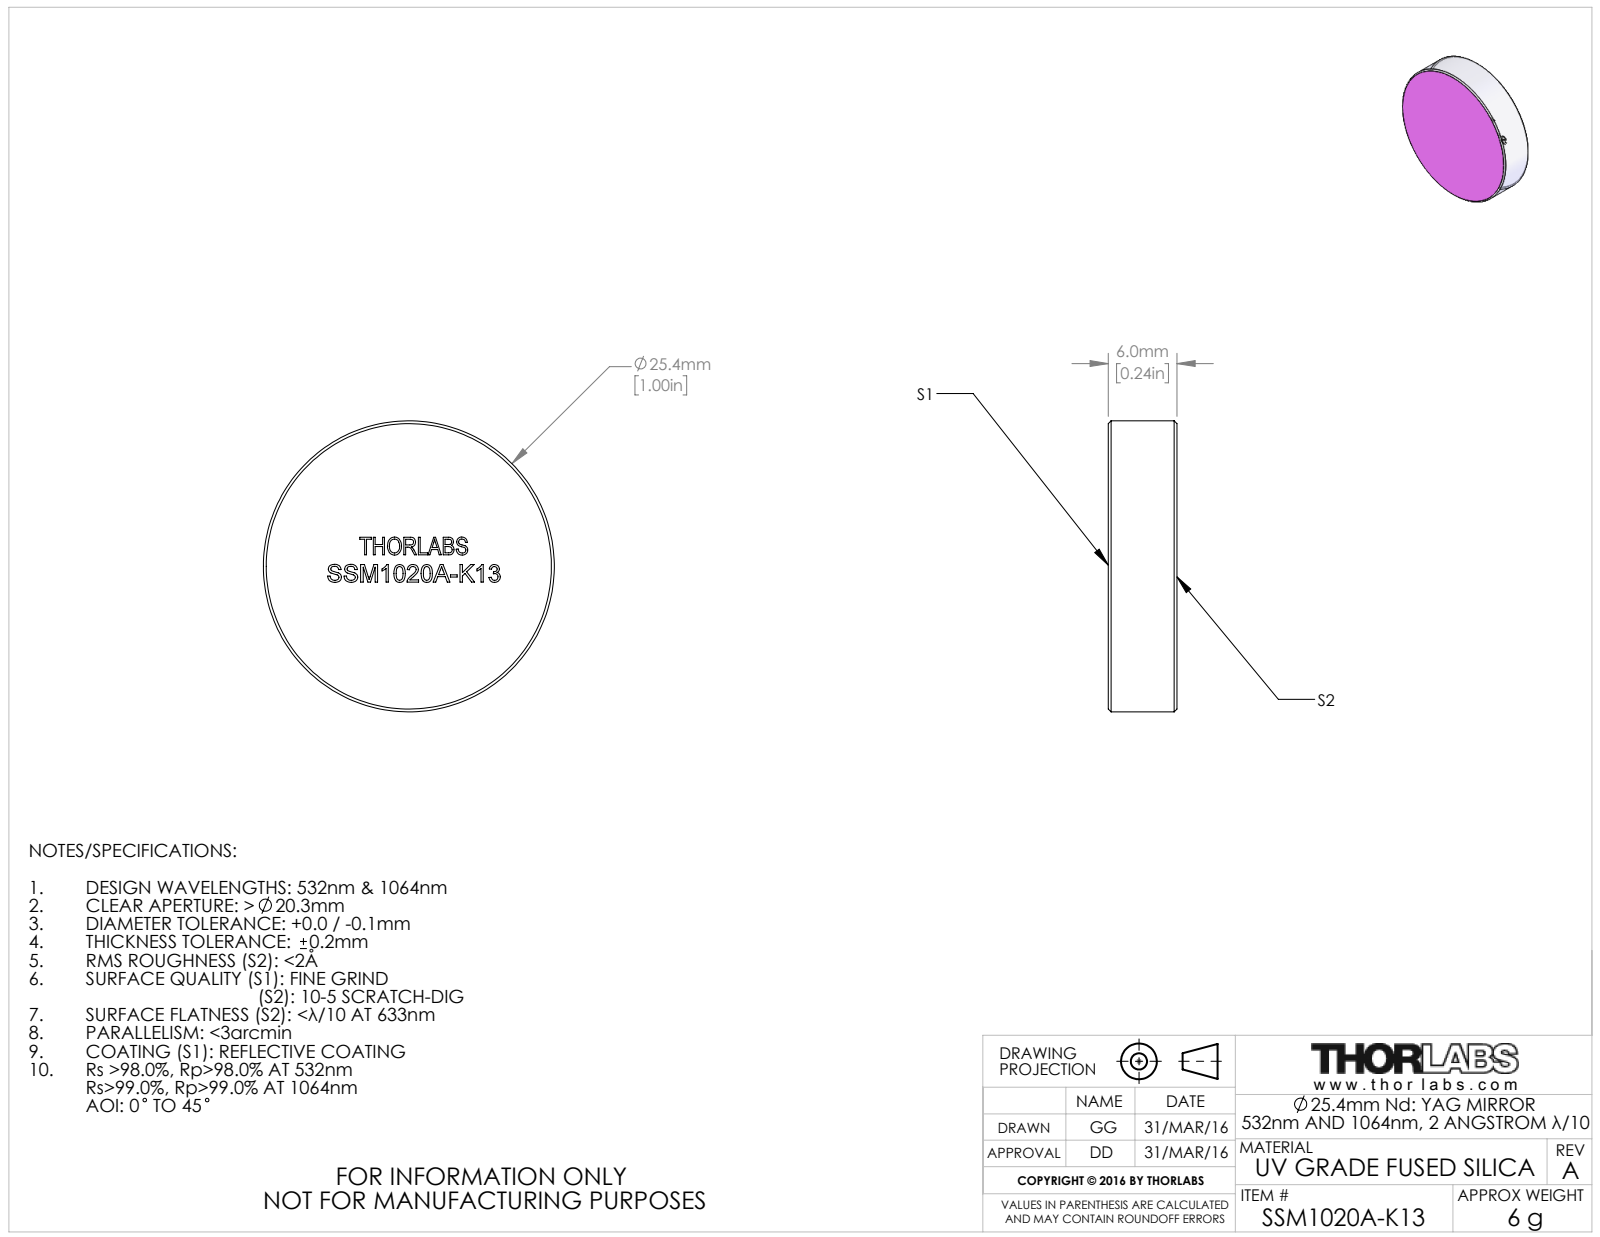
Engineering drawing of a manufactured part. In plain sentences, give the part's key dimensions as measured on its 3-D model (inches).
The part is named "TTN094211-E0W". Its 3-D file was written by "SolidWorks 2014 (CONFIG_CONTROL_DESIGN)". It is 1 solid with 36 faces: 30 planar, 2 cylindrical and 4 other. Overall it measures 1 by 1 by 0.236 inches. Its volume is 0.185 cubic inches and its surface area 2.276 square inches. Round bosses or shafts: 1 of diameter 1. The main face-to-face distances are 0.236.
